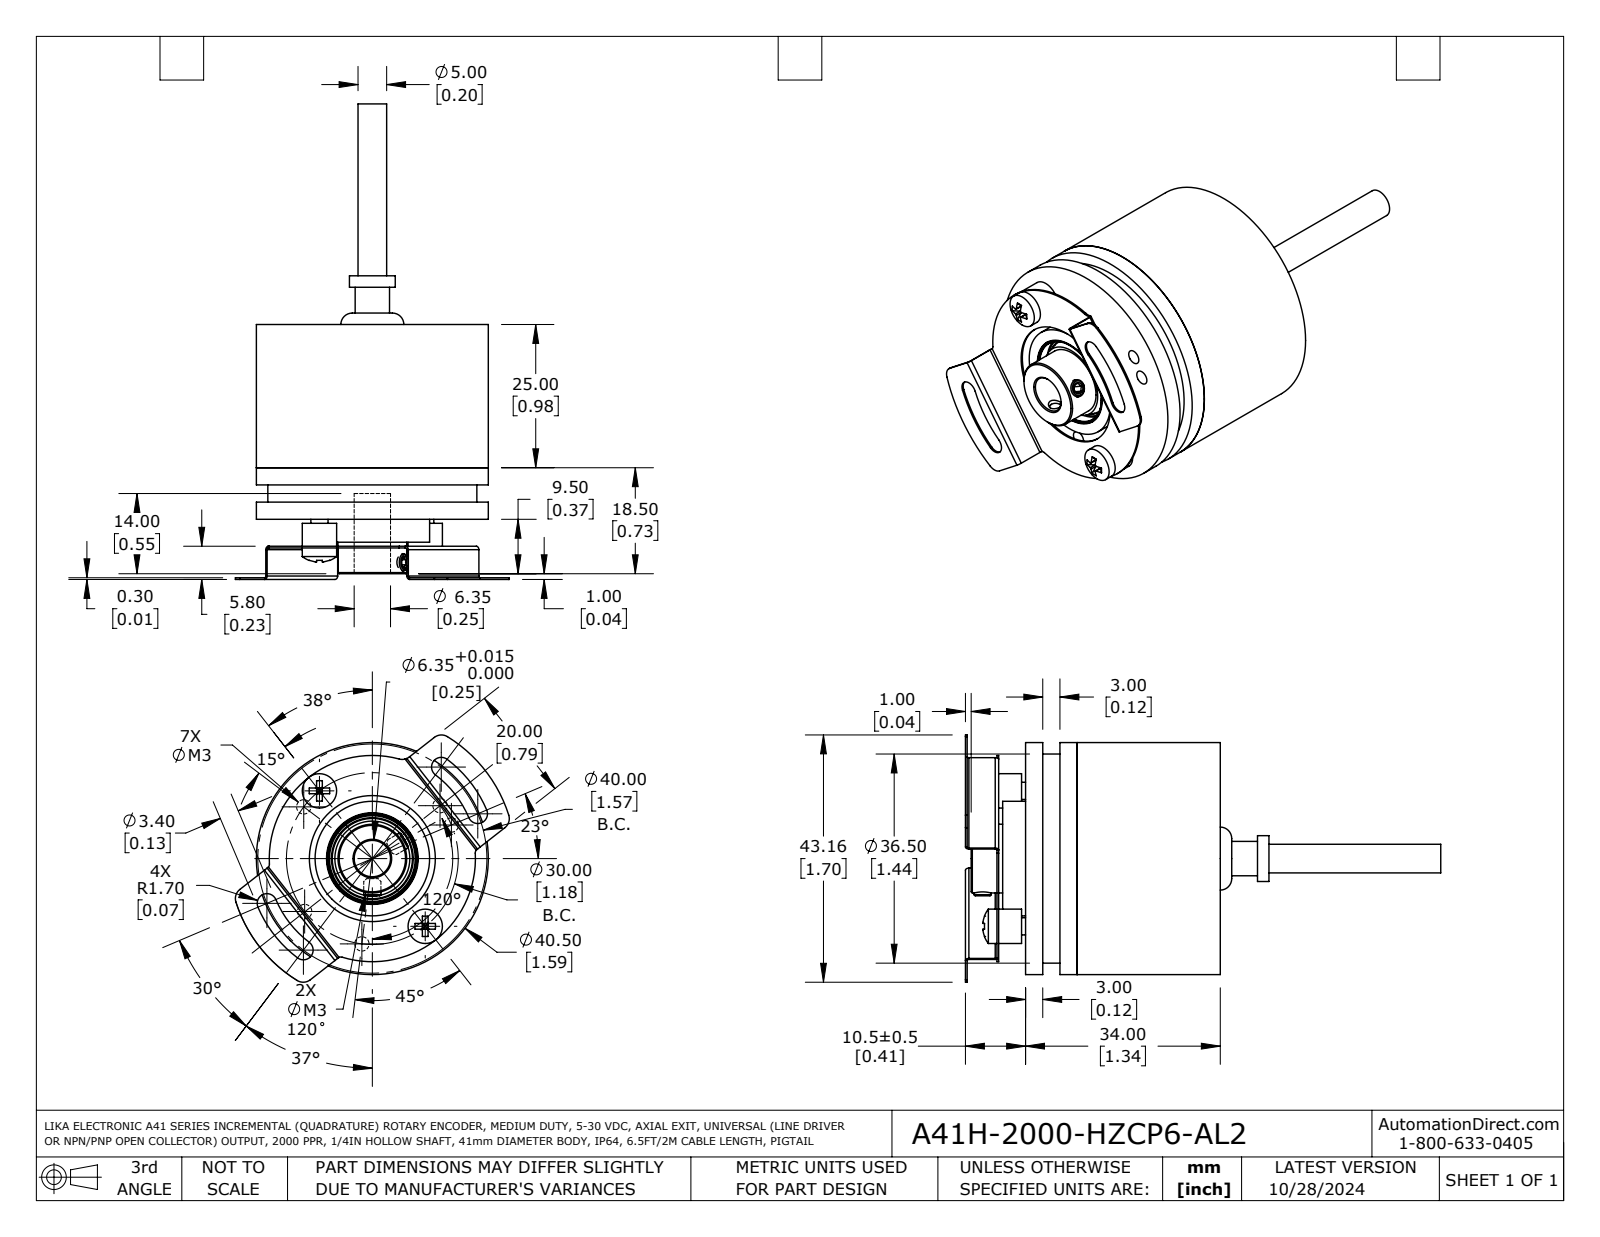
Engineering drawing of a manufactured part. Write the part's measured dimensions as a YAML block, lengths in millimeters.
part_name: "A41H-2000-HZCP6-AL2"
step_written_by: "SolidWorks 2021 (AUTOMOTIVE_DESIGN)"
units: millimeters
bodies: {solids: 15, faces: 465, planar: 139, cylindrical: 186, other: 140}
overall_size: [83, 47.8, 43.2]
volume: 19450
surface_area: 20890
round_holes:
  - {diameter: 2.5, count: 9}
  - {diameter: 1.6, count: 7}
  - {diameter: 4, count: 3}
  - {diameter: 2.2, count: 2}
  - {diameter: 3.2, count: 2}
  - {diameter: 3.5, count: 2}
  - {diameter: 4.3, count: 1}
  - {diameter: 6.4, count: 1}
  - {diameter: 7.5, count: 1}
  - {diameter: 13, count: 1}
  - {diameter: 15.3, count: 1}
  - {diameter: 15.5, count: 1}
round_bosses_or_shafts:
  - {diameter: 3, count: 4}
  - {diameter: 6, count: 3}
  - {diameter: 3.8, count: 2}
  - {diameter: 2, count: 2}
  - {diameter: 40.5, count: 1}
  - {diameter: 38, count: 1}
  - {diameter: 37, count: 1}
  - {diameter: 36.5, count: 1}
partial_cylinders:
  - {radius: 1, count: 14}
  - {radius: 0.2, count: 8}
  - {radius: 2, count: 5}
  - {radius: 0.3, count: 4}
  - {radius: 0.6, count: 4}
  - {radius: 1.7, count: 4}
  - {radius: 0.8, count: 3}
  - {radius: 18, count: 1}
face_to_face_distances: [3, 11, 34, 23, 5, 31, 2, 22, 1, 20]
hole_center_spacings: [15, 17, 21.2, 2.8, 3, 21.3, 24, 26]
